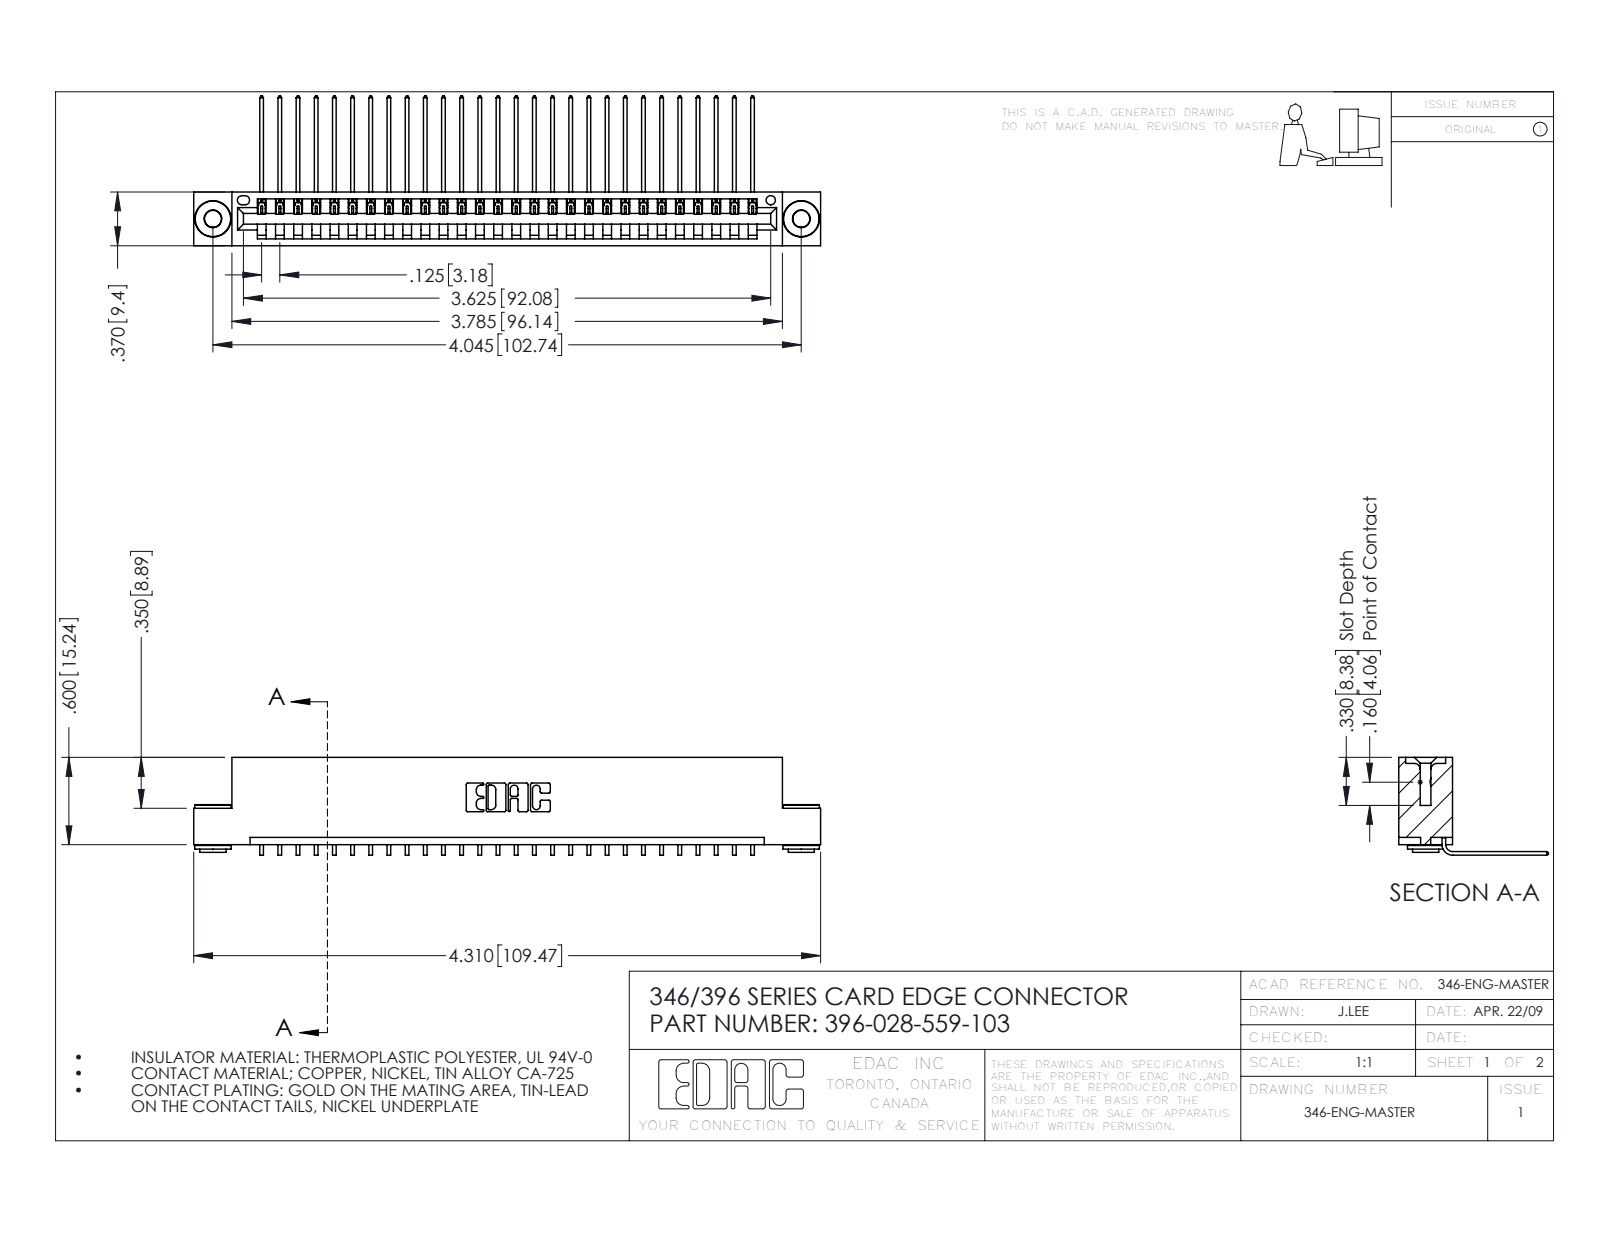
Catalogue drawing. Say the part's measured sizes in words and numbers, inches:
The part is named "346 Part_Flush Mounting Lugs - 0.156 Dia-TH; 345-250-002_345-250-002-102; 396-028-559-103; 345-292-001_558 559 Tail - 1". Its 3-D file was written by "SolidWorks 2016 (CONFIG_CONTROL_DESIGN)". It is 31 solids with 1840 faces: 1262 planar, 570 cylindrical and 8 other. Overall it measures 4.31 by 1.03 by 0.673 inches. Its volume is 0.64 cubic inches and its surface area 21.3 square inches. Round holes: 2 of diameter 0.116, 2 of diameter 0.156, 1 of diameter 0.064. Round bosses or shafts: 2 of diameter 0.25, 2 of diameter 0.18, 2 of diameter 0.136. Partial cylindrical surfaces (rounded edges, fillets, slot ends): 56 of radius 0.006, 22 of radius 0.01, 6 of radius 0.007, 6 of radius 0.031, 3 of radius 0.026, 2 of radius 0.031, 2 of radius 0.04, 1 of radius 0.014. The main face-to-face distances are 0.048, 0.322, 0.37, 0.25, 0.025, 0.072, 0.298, 0.148, 0.222, 0.1. The hole center spacings are 0.246, 3.837, 4.045.
